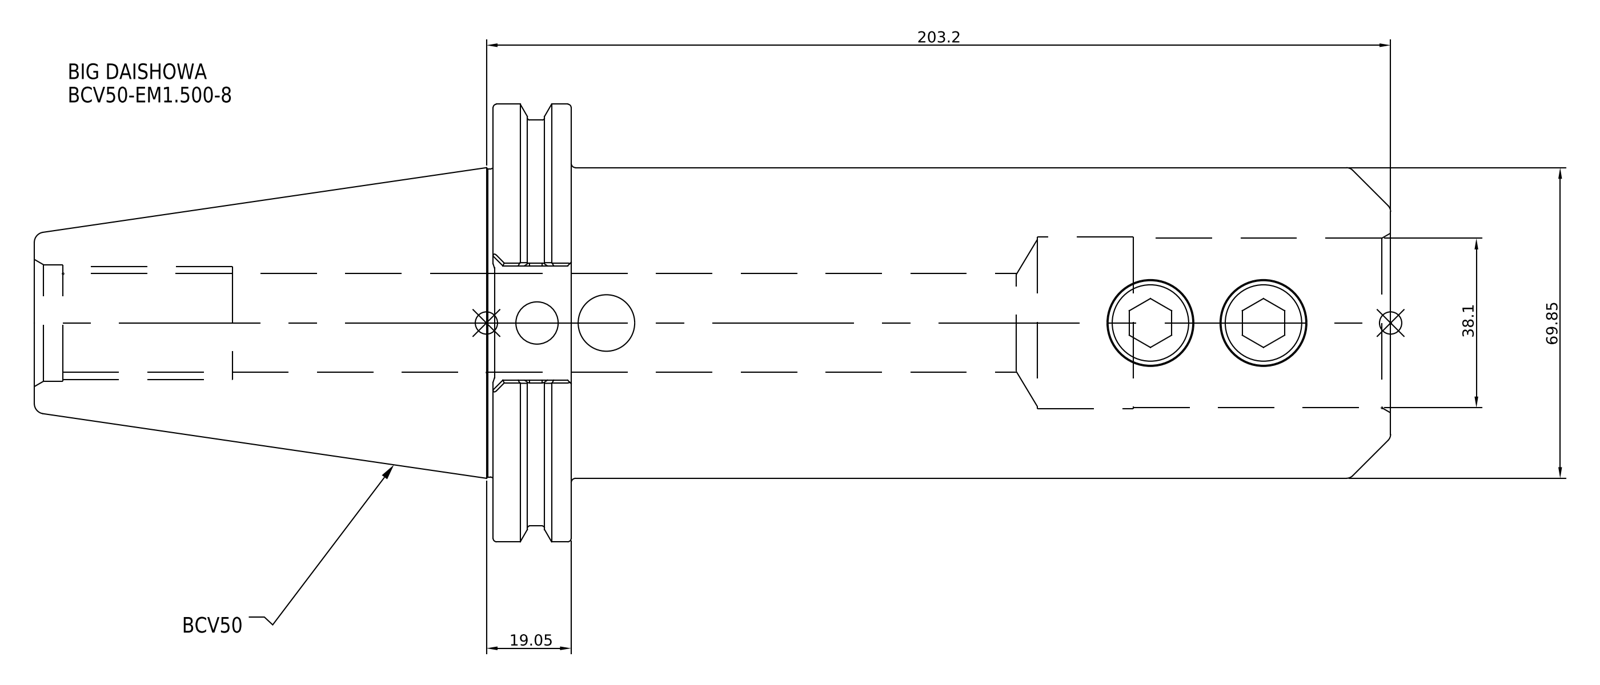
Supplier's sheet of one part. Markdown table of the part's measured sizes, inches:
| quantity | value |
| --- | --- |
| part name | BCV50-EM1_500-8 |
| STEP written by | SolidWorks 2021 (CONFIG_CONTROL_DESIGN) |
| units | inches |
| bodies | 1 solid, 27 faces (7 planar, 12 cylindrical, 8 other) |
| overall size | 12 × 3.875 × 3.875 |
| volume | 54.13 in³ |
| surface area | 149.9 in² |
| round holes (diameter × count) | 1.5 × 1 |
| round bosses / shafts (diameter × count) | 3.875 × 1, 3.594 × 1, 2.75 × 1 |
| main face-to-face distances | 0.691, 4.75, 4.059, 0.63, 1.321, 5.38, 6.62, 7.25, 7.941, 12 |
